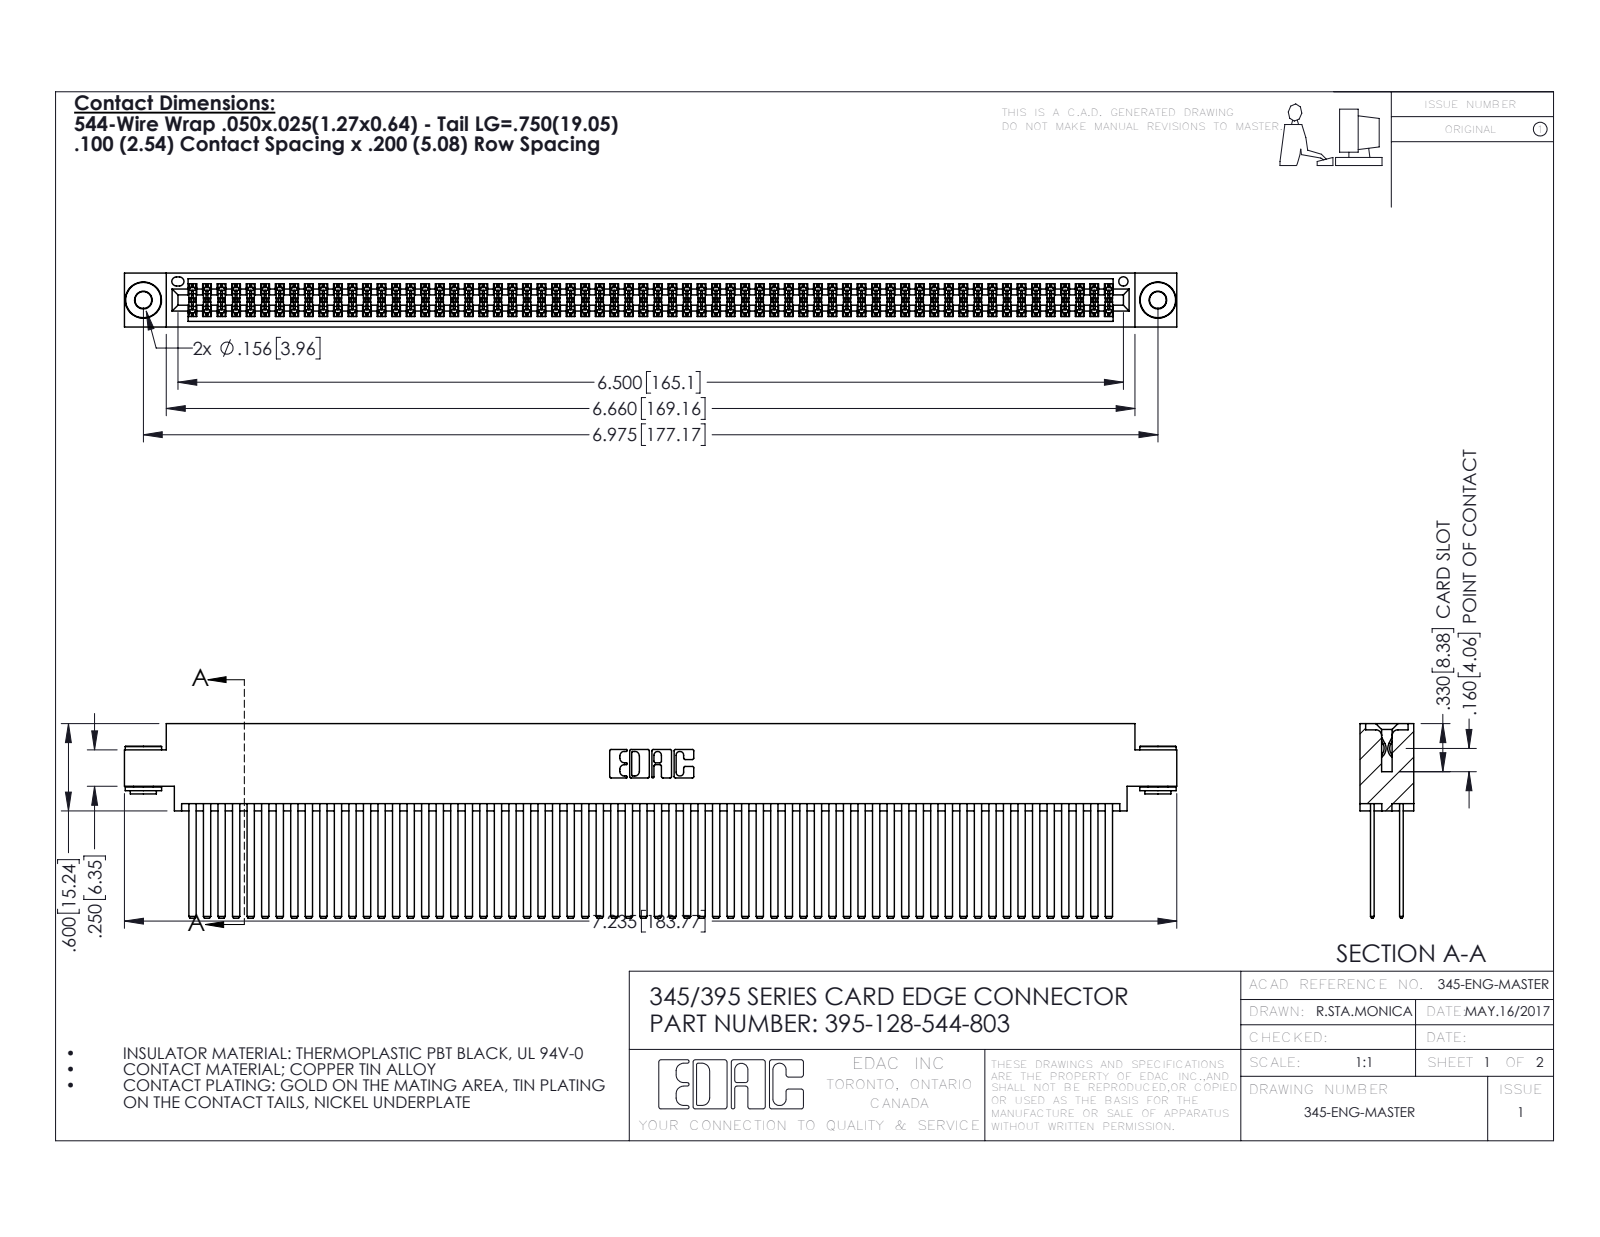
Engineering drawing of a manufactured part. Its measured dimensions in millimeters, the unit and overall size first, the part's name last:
Units: millimetres
Overall size (bounding box): 183.8 × 34 × 9.4
Round holes (diameter × count): ⌀2.9 ×2, ⌀4 ×2, ⌀1.6 ×1
Round bosses / shafts (diameter × count): ⌀6.4 ×2, ⌀4.6 ×2, ⌀3.5 ×2
Partial cylindrical surfaces — rounded edges, fillets, slot ends (radius × count): R0.2 ×192, R0.3 ×22, R0.2 ×6, R0.8 ×6, R0.7 ×3, R0.4 ×2, R0.5 ×2, R0.6 ×2
Main face-to-face distances: 5.1, 0.6, 1.8, 2.5, 6.9, 7.6, 5.7, 4.4, 9.4, 3.8
Hole centre spacings: 6.9, 171.2, 177.2
Volume: 19 760 mm³ · Surface area: 35 240 mm²
Bodies: 131 solids, 5800 faces (3806 planar, 1986 cylindrical, 8 other)
Part name (STEP PRODUCT): 345-292-001_345-293-144; 345 Part_0.170 Offset - 0.156 Dia-TH; 345-250-002_345-250-002-102; 395-128-544-803
STEP written by: SolidWorks 2016 (CONFIG_CONTROL_DESIGN)
